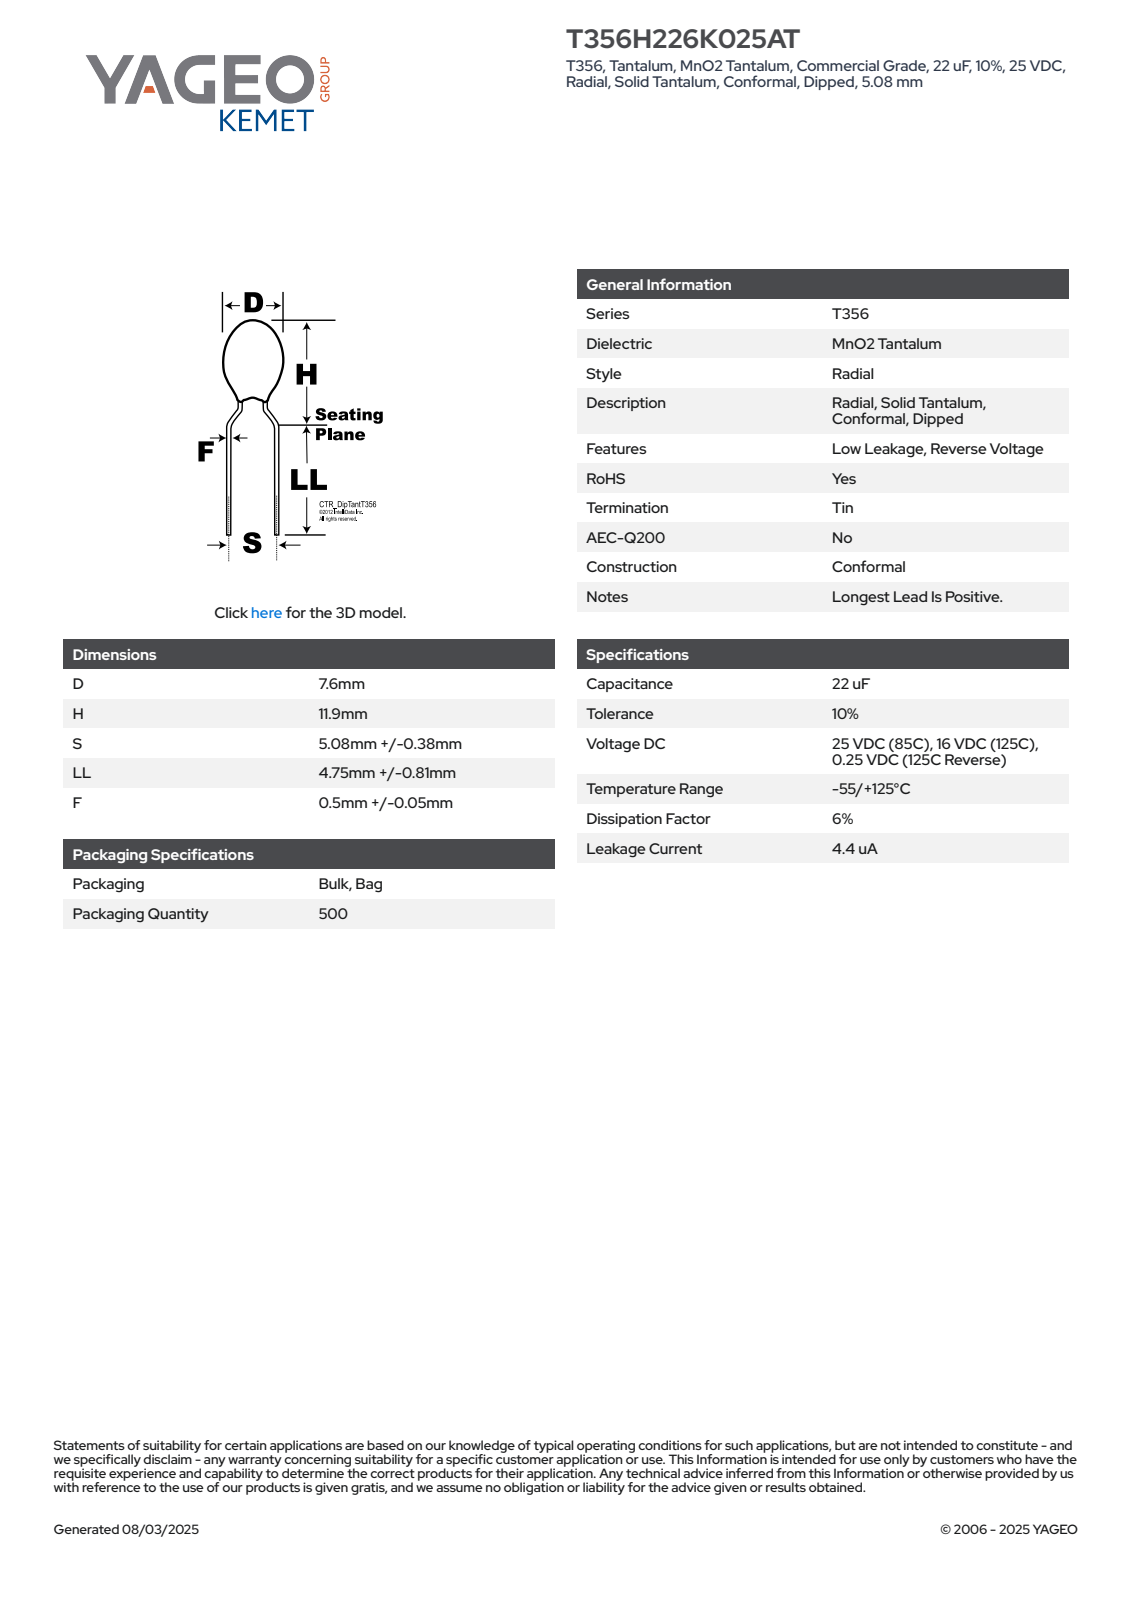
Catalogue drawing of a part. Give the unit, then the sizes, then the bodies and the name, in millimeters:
Units: millimetres
Overall size (bounding box): 17.46 × 7.6 × 7.6
Round bosses / shafts (diameter × count): ⌀0.55 ×6, ⌀7.6 ×1
Partial cylindrical surfaces — rounded edges, fillets, slot ends (radius × count): R3.79 ×1
Main face-to-face distances: 8.3, 9.16, 17.46, 14.69, 5.53, 2.77, 13.48, 4.32, 1.21, 3.98
Volume: 335 mm³ · Surface area: 275 mm²
Bodies: 1 solid, 96 faces (27 planar, 18 cylindrical, 51 other)
Part name (STEP PRODUCT): CTR_T356_D7.6H11.9S5.08LL5.56F0.55
STEP written by: SolidWorks 2014 (AUTOMOTIVE_DESIGN)
